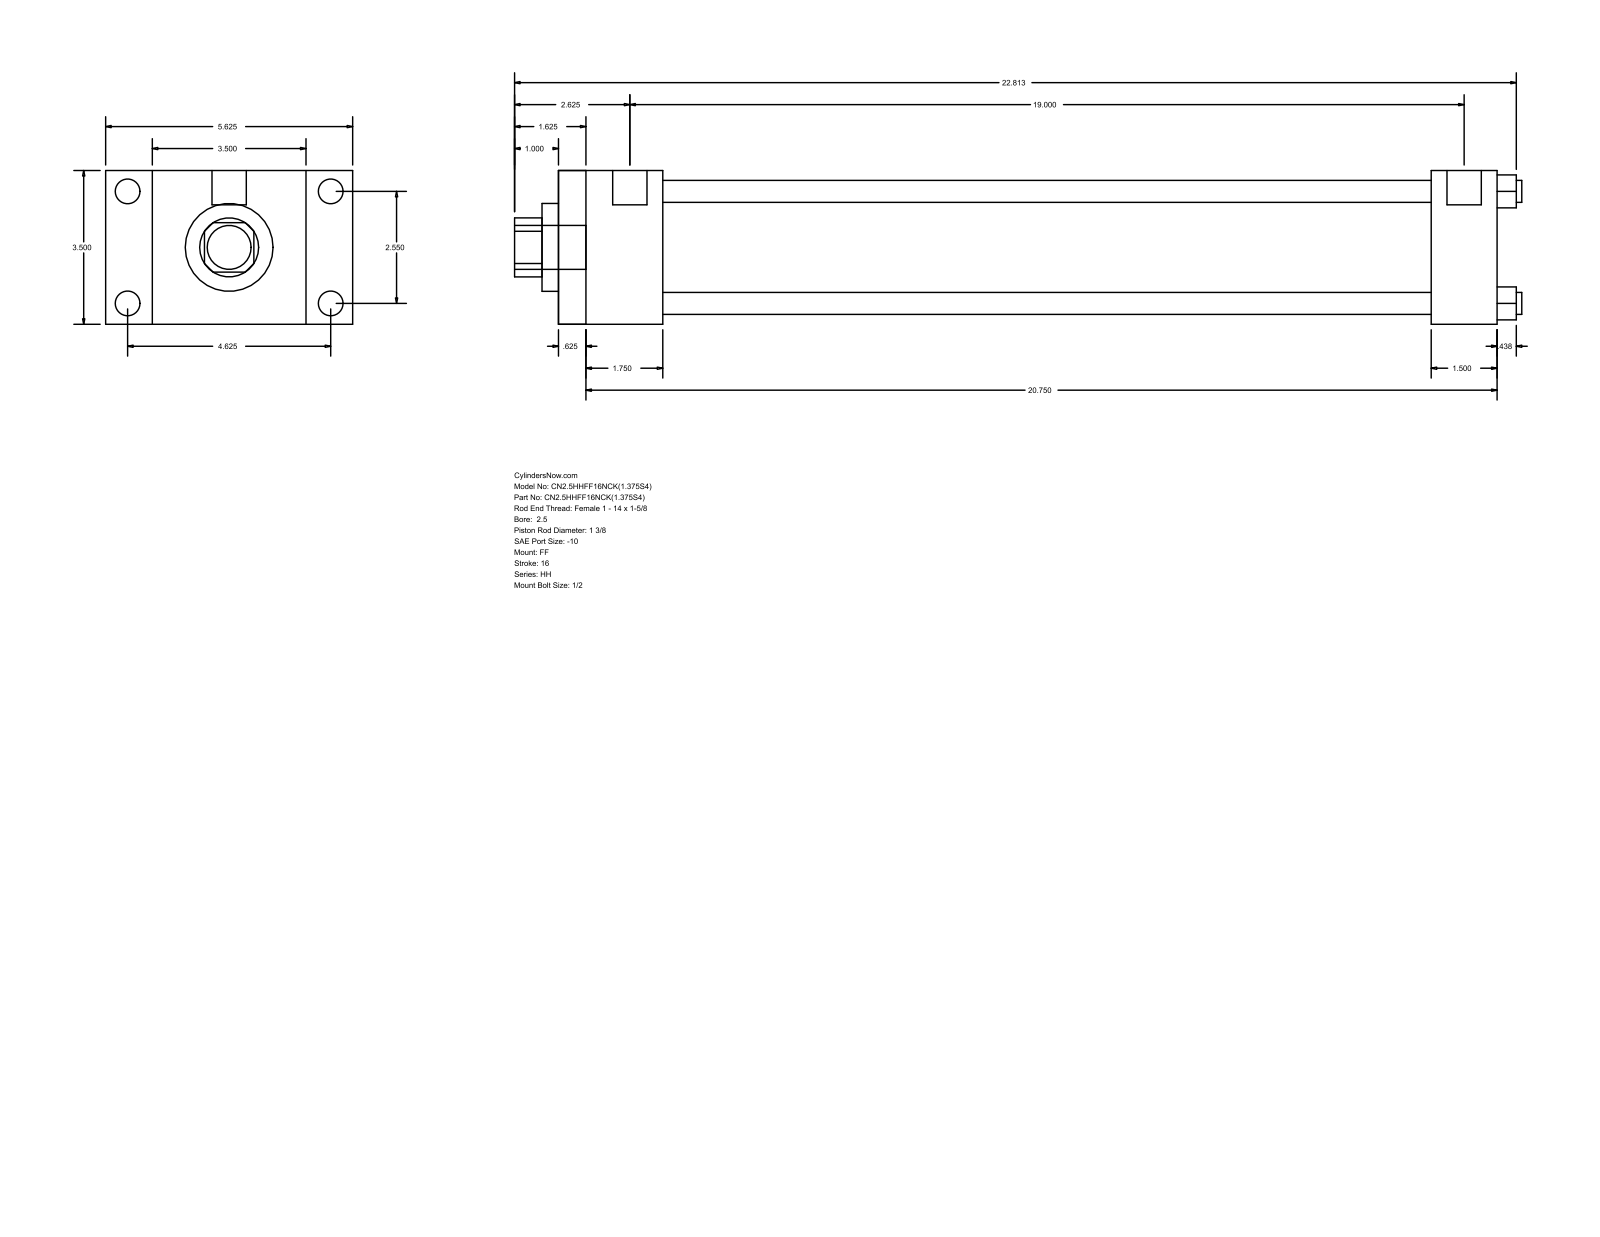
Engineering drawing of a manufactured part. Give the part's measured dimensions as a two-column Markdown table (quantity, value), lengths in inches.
| quantity | value |
| --- | --- |
| part name | HH_FF__0250_1.375 |
| STEP written by | GSSL Pune (CONFIG_CONTROL_DESIGN) |
| units | inches |
| bodies | 0 solids, 92 faces (64 planar, 28 cylindrical, 0 other) |
| overall size | 22.937 × 5.625 × 3.5 |
| round holes (diameter × count) | 0.5 × 4, 1.375 × 1, 2 × 1, 2.875 × 1 |
| round bosses / shafts (diameter × count) | 0.563 × 4, 0.219 × 4, 0.781 × 2, 1 × 1 |
| partial cylindrical surfaces (radius × count) | 0.672 × 1 |
| main face-to-face distances | 3.5, 21.375, 0.625, 20.75, 2.375, 1.75, 19, 19.875, 19.25, 17.5 |
| hole center spacings | 1.803, 2.55, 3.606 |
